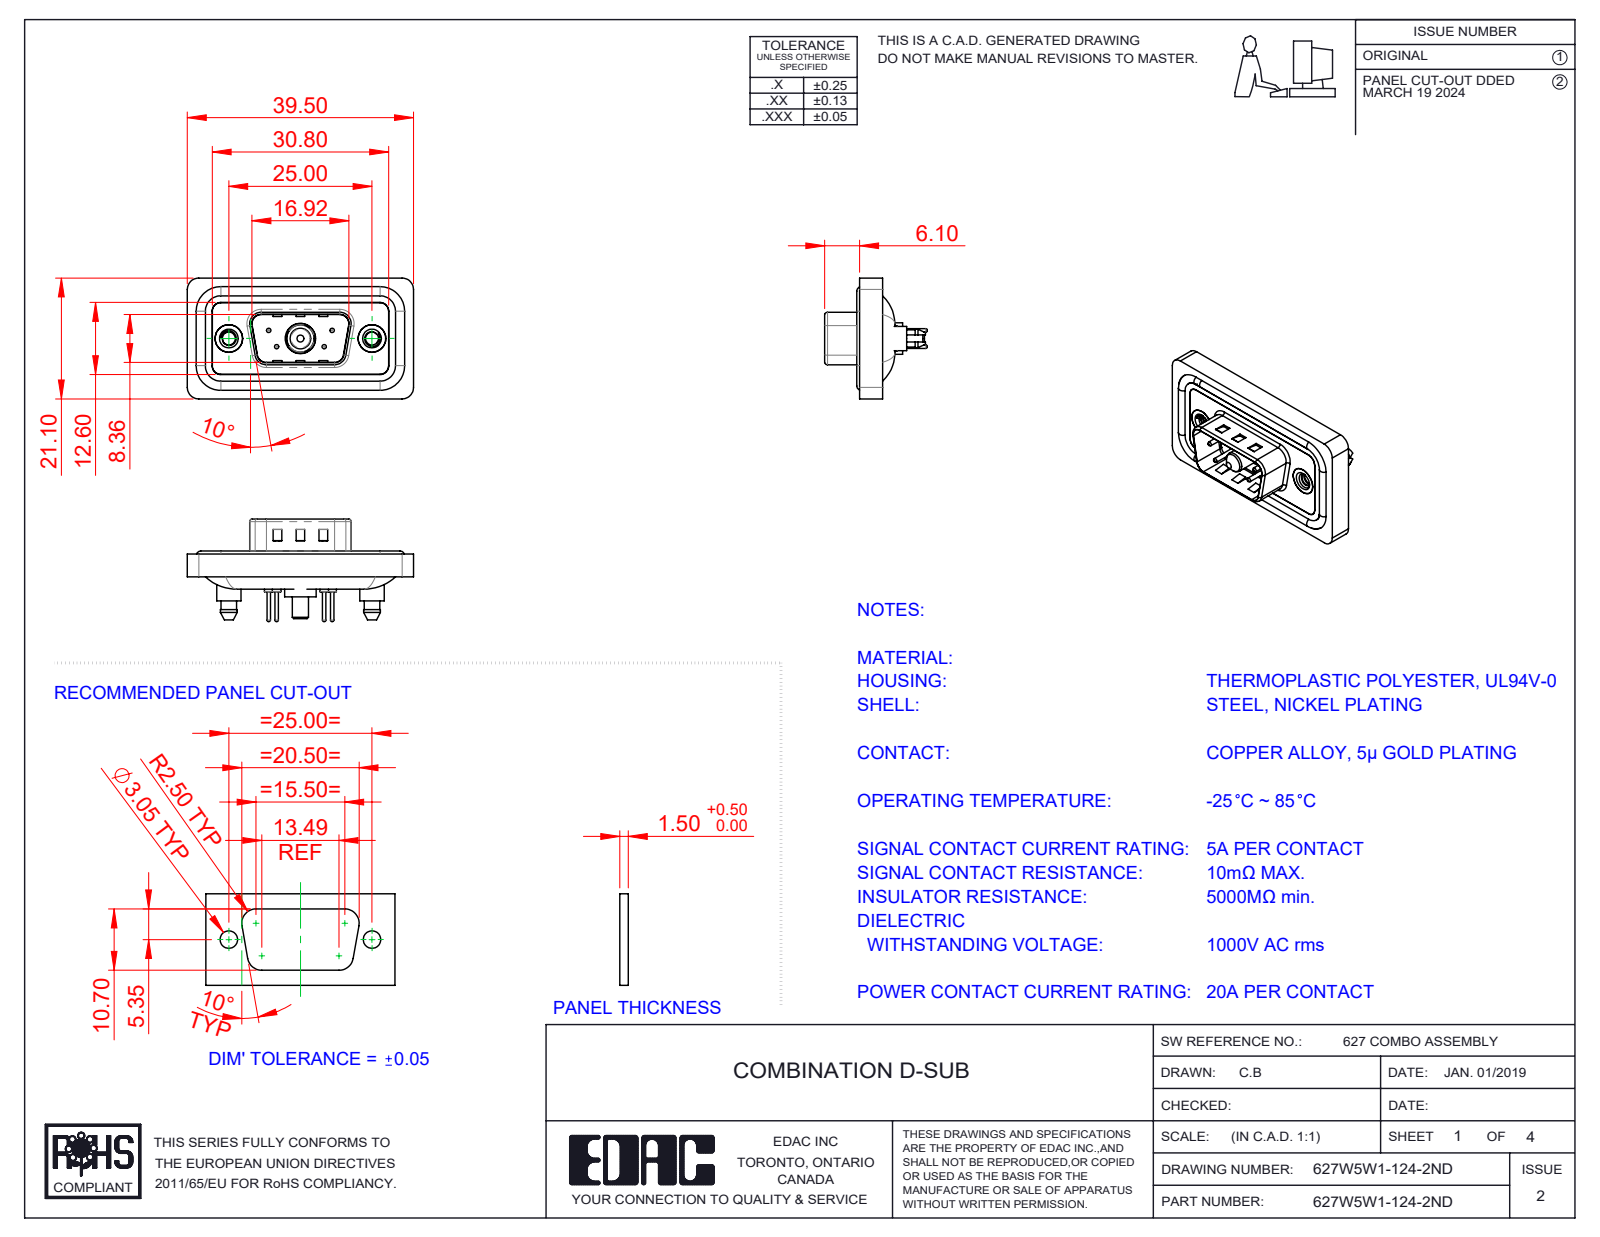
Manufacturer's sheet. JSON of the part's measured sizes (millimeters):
{"part_name": "627Combo Contact Row 2_24; 627Combo Waterproof Housing_09 Contacts; 627Combo Housing_5W1; 627Combo Contact Row 1_24 (+6 more)", "step_written_by": "SolidWorks 2023 (CONFIG_CONTROL_DESIGN)", "units": "millimeters", "bodies": {"solids": 13, "faces": 656, "planar": 199, "cylindrical": 295, "other": 162}, "overall_size": [39.5, 21.1, 17.9], "volume_mm3": 4522, "surface_area_mm2": 7277, "round_holes": [[0.75, 4], [1.6, 4], [2, 4], [2.26, 2], [4, 2], [4.8, 2], [5, 2], [4.85, 1], [5.3, 1]], "round_bosses_or_shafts": [[1.6, 4], [1.5, 4], [0.6, 4], [5.4, 2], [4.9, 2], [4.25, 2], [5.5, 1], [5.2, 1]], "partial_cylinders_radius": [[1.5, 24], [2, 18], [1.6, 10], [0.5, 8], [0.25, 4], [0.6, 4], [0.65, 4], [0.9, 4]], "face_to_face_distances": [0.4, 1.1, 2.9, 1.6, 1.5, 3.1, 0.5, 2.5, 4, 0.8], "hole_center_spacings": [3.16, 5.72, 7.1, 12.5, 18.1, 4.39, 4.4, 8.31]}
